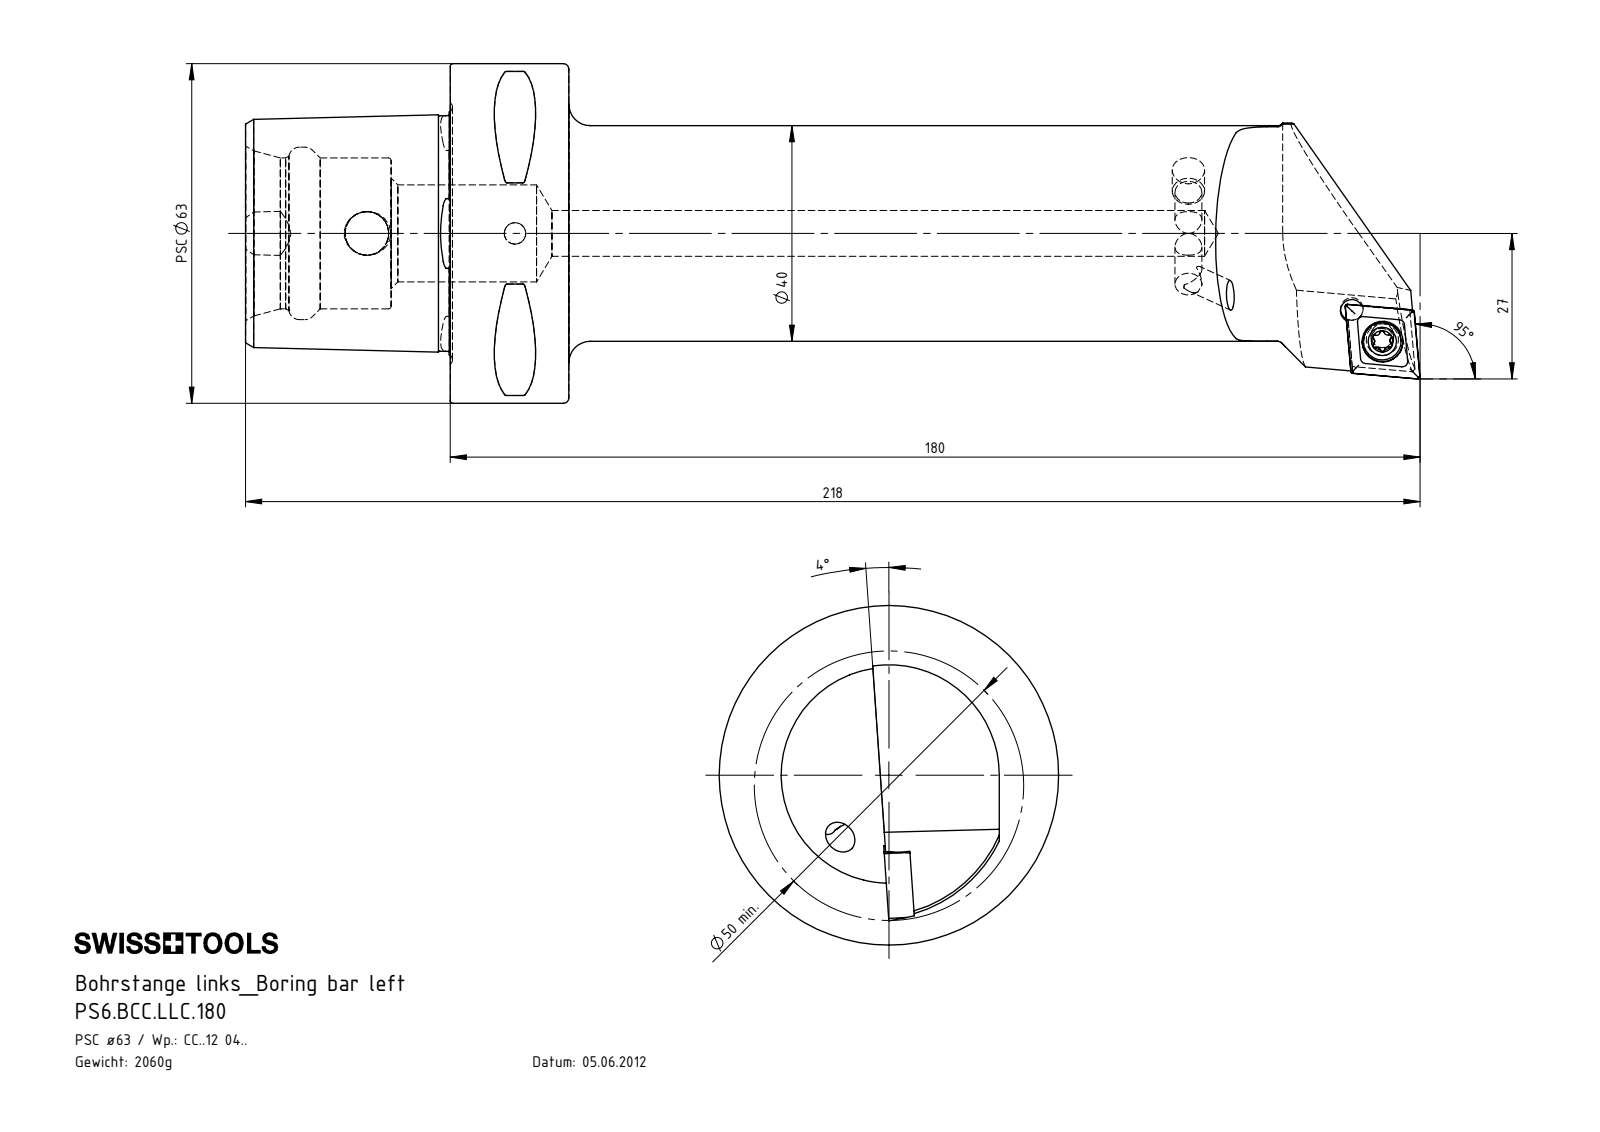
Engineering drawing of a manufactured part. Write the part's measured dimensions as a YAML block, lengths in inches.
part_name: "PS6-BCC.LLC.180; KVT_MB_600_050; WCC-ER2.001.010_A; CCMT120404 (+1 more)"
step_written_by: "SolidWorks 2012 (CONFIG_CONTROL_DESIGN)"
units: inches
bodies: {solids: 5, faces: 282, planar: 49, cylindrical: 75, other: 158}
overall_size: [8.583, 2.48, 2.48]
volume: 16.01
surface_area: 66.59
round_holes:
  - {diameter: 0.157, count: 2}
  - {diameter: 0.165, count: 2}
  - {diameter: 0.197, count: 2}
  - {diameter: 0.217, count: 1}
  - {diameter: 0.236, count: 1}
  - {diameter: 0.299, count: 1}
  - {diameter: 0.319, count: 1}
  - {diameter: 0.335, count: 1}
  - {diameter: 0.709, count: 1}
  - {diameter: 1.102, count: 1}
  - {diameter: 1.26, count: 1}
round_bosses_or_shafts:
  - {diameter: 0.197, count: 2}
  - {diameter: 2.48, count: 1}
  - {diameter: 1.575, count: 1}
  - {diameter: 0.276, count: 1}
partial_cylinders:
  - {radius: 0.02, count: 8}
  - {radius: 0.015, count: 6}
  - {radius: 0.027, count: 6}
  - {radius: 0.236, count: 2}
  - {radius: 0.807, count: 1}
  - {radius: 0.984, count: 1}
face_to_face_distances: [0.866, 1.496, 2.362, 0.98, 1.063, 0.433, 1.299, 0.176, 2.197, 1.488]
hole_center_spacings: [0.316, 0.319, 1.083]
